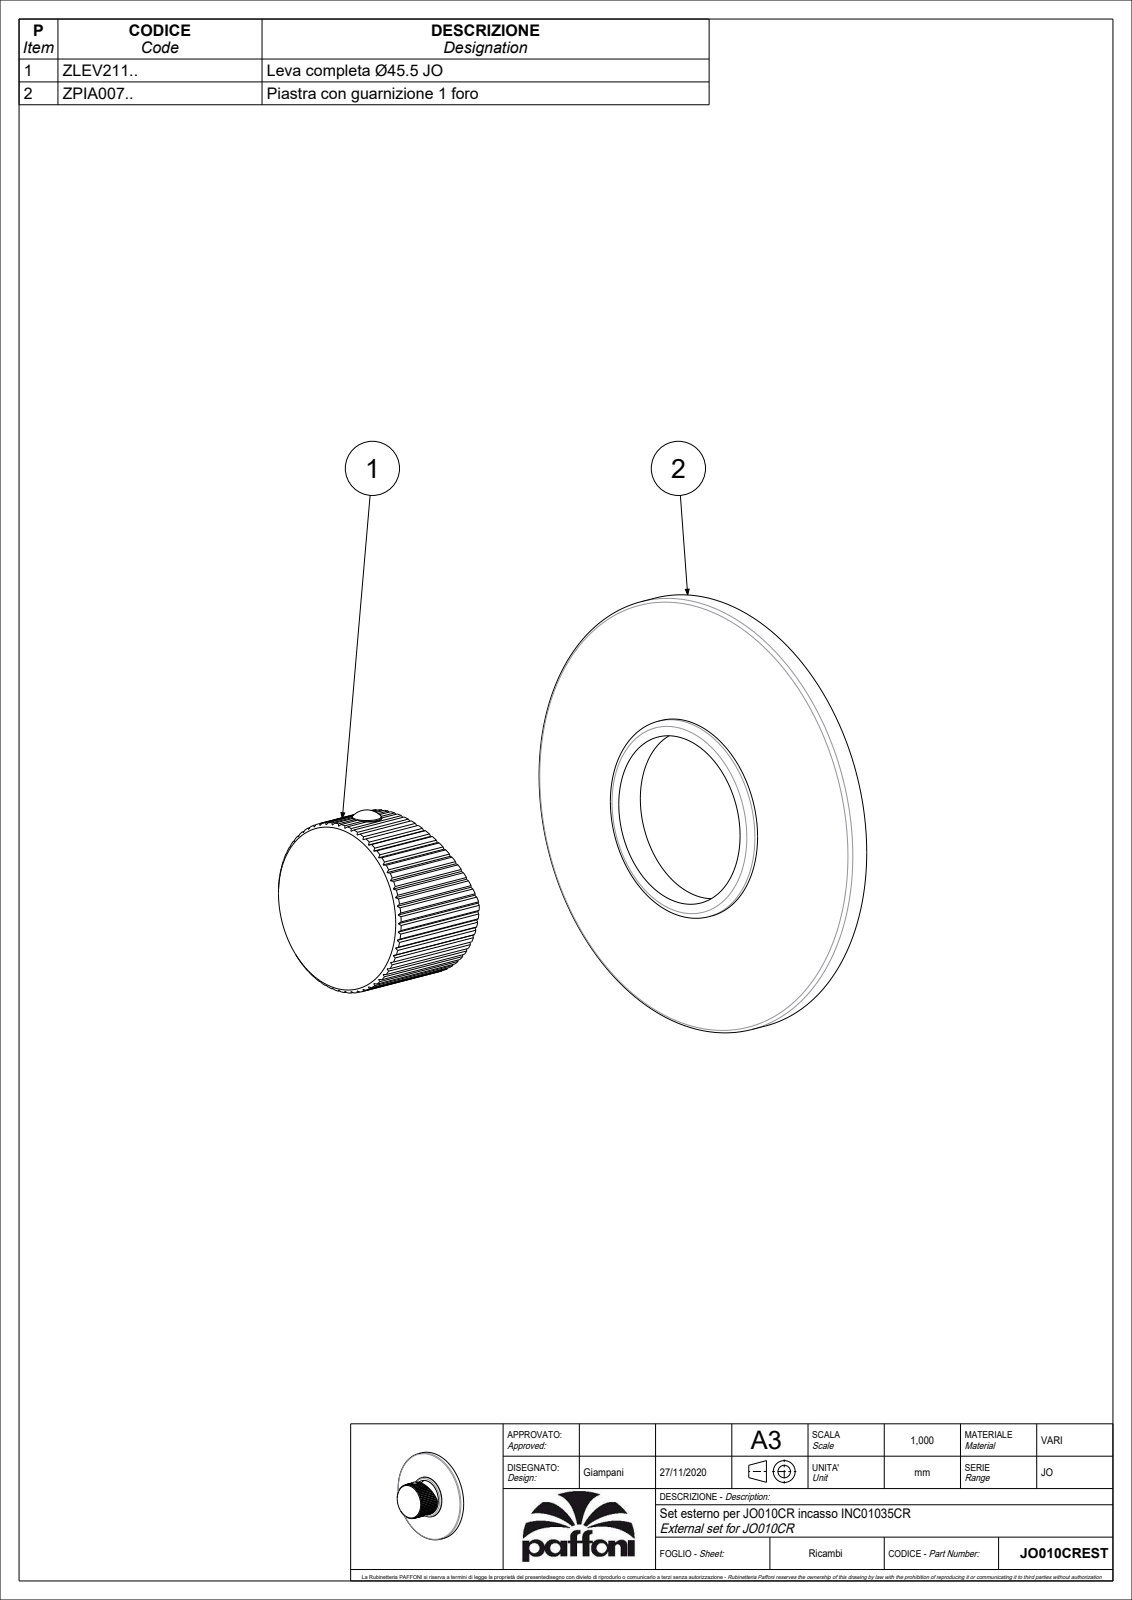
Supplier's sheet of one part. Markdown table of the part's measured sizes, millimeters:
| quantity | value |
| --- | --- |
| part name | JO010CREST |
| STEP written by | CREO PARAMETRIC BY PTC INC, 2020044 (CONFIG_CONTROL_DESIGN) |
| units | millimeters |
| bodies | 2 solids, 354 faces (196 planar, 119 cylindrical, 39 other) |
| overall size | 116 × 116 × 43.9 |
| volume | 23 160 mm³ |
| surface area | 37 447 mm² |
| round holes (diameter × count) | 3 × 1, 10.5 × 1, 42 × 1, 45 × 1, 50 × 1, 114 × 1 |
| round bosses / shafts (diameter × count) | 116 × 1, 53 × 1, 16 × 1, 7.6 × 1, 5.5 × 1, 5 × 1 |
| partial cylindrical surfaces (radius × count) | 4 × 1, 22.75 × 1 |
| main face-to-face distances | 4, 29, 11.5, 40.5, 2.5, 7.5, 9, 31.5, 1.5, 3.5 |
